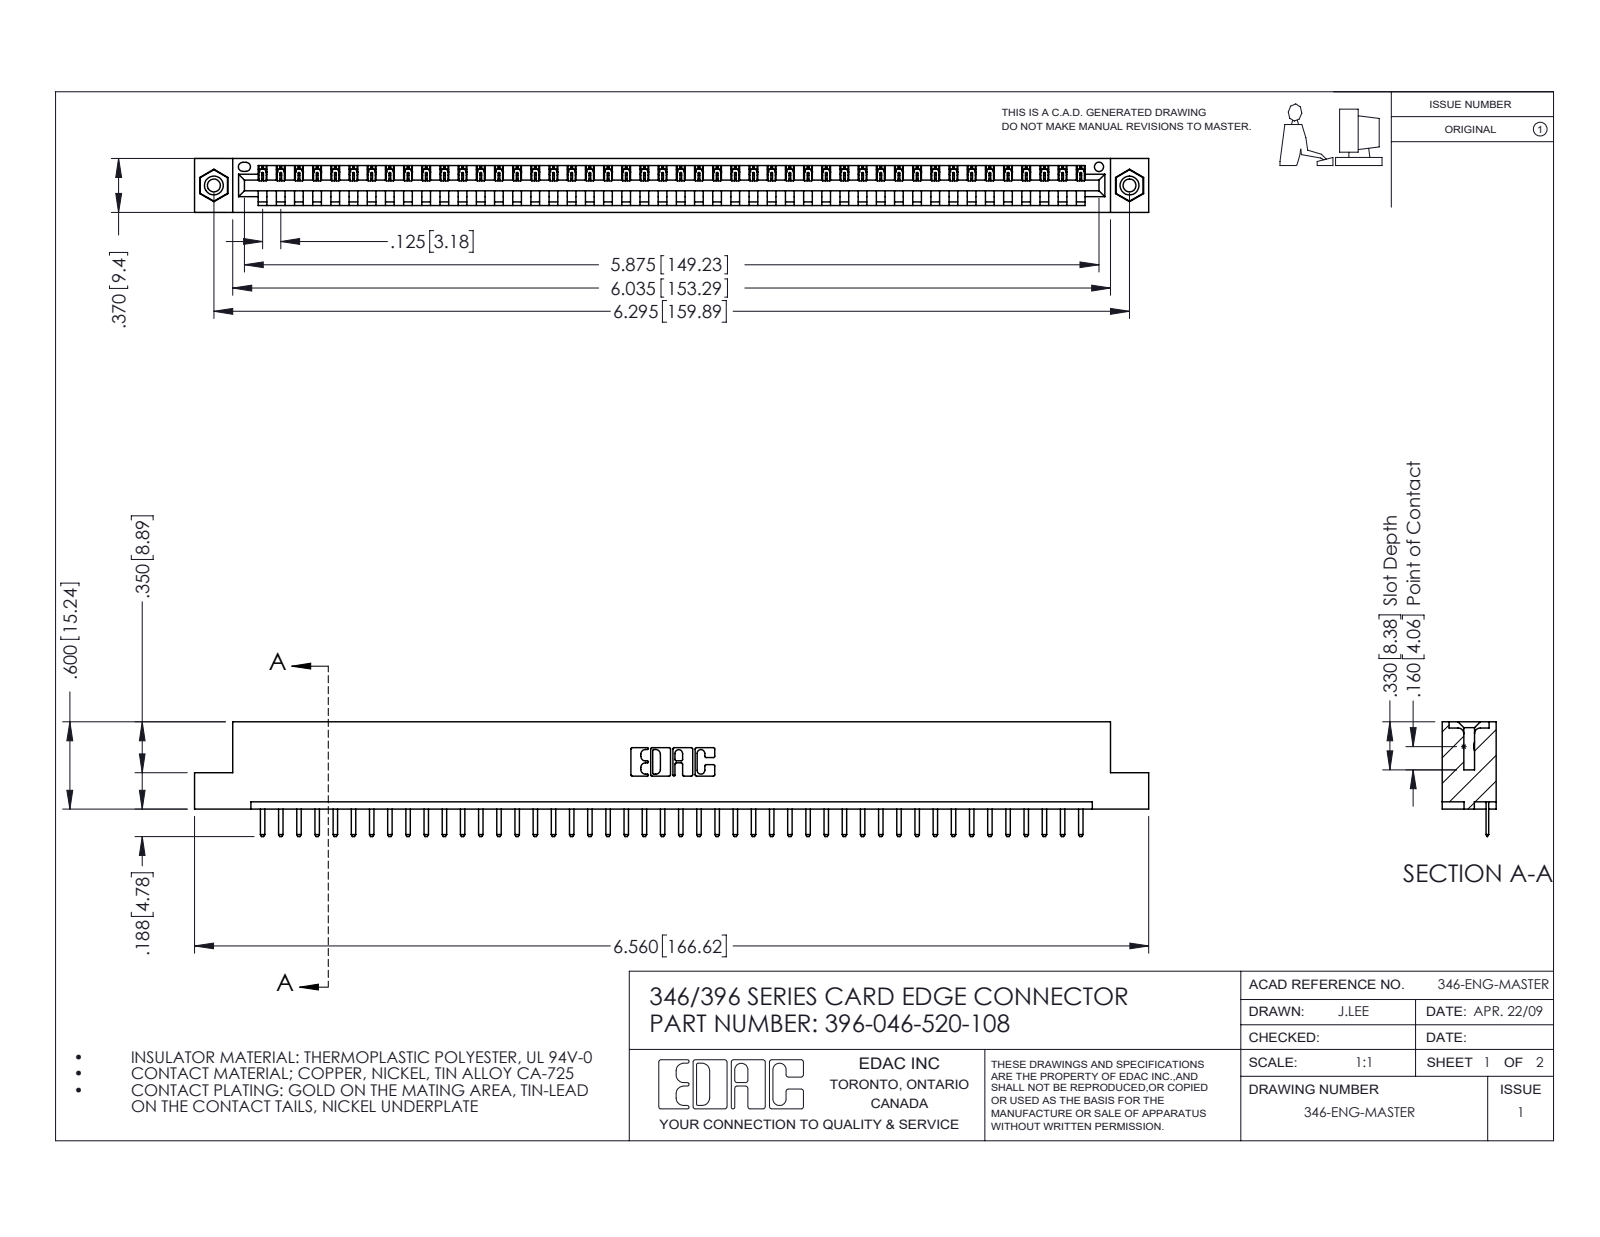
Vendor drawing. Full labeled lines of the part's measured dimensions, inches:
Part name (STEP PRODUCT): 345-292-001_345-293-120; 346 Part_Flush Mounting Lugs - 0.156 Dia-TI; 345-250-001_345-250-003-102; 396-046-520-108
STEP written by: SolidWorks 2016 (CONFIG_CONTROL_DESIGN)
Units: inches
Bodies: 49 solids, 3034 faces (2040 planar, 978 cylindrical, 16 other)
Overall size (bounding box): 6.56 × 0.788 × 0.37
Volume: 0.967 in³ · Surface area: 30.1 in²
Round holes (diameter × count): ⌀0.089 ×2, ⌀0.125 ×2, ⌀0.156 ×2, ⌀0.064 ×1
Round bosses / shafts (diameter × count): ⌀0.155 ×2
Partial cylindrical surfaces — rounded edges, fillets, slot ends (radius × count): R0.01 ×94, R0.006 ×92, R0.01 ×22, R0.007 ×6, R0.031 ×6, R0.026 ×3, R0.031 ×2, R0.04 ×2
Main face-to-face distances: 0.048, 0.322, 0.37, 0.25, 0.148, 0.222, 0.1, 0.174, 0.072, 0.298
Hole centre spacings: 0.246, 6.086, 6.295
